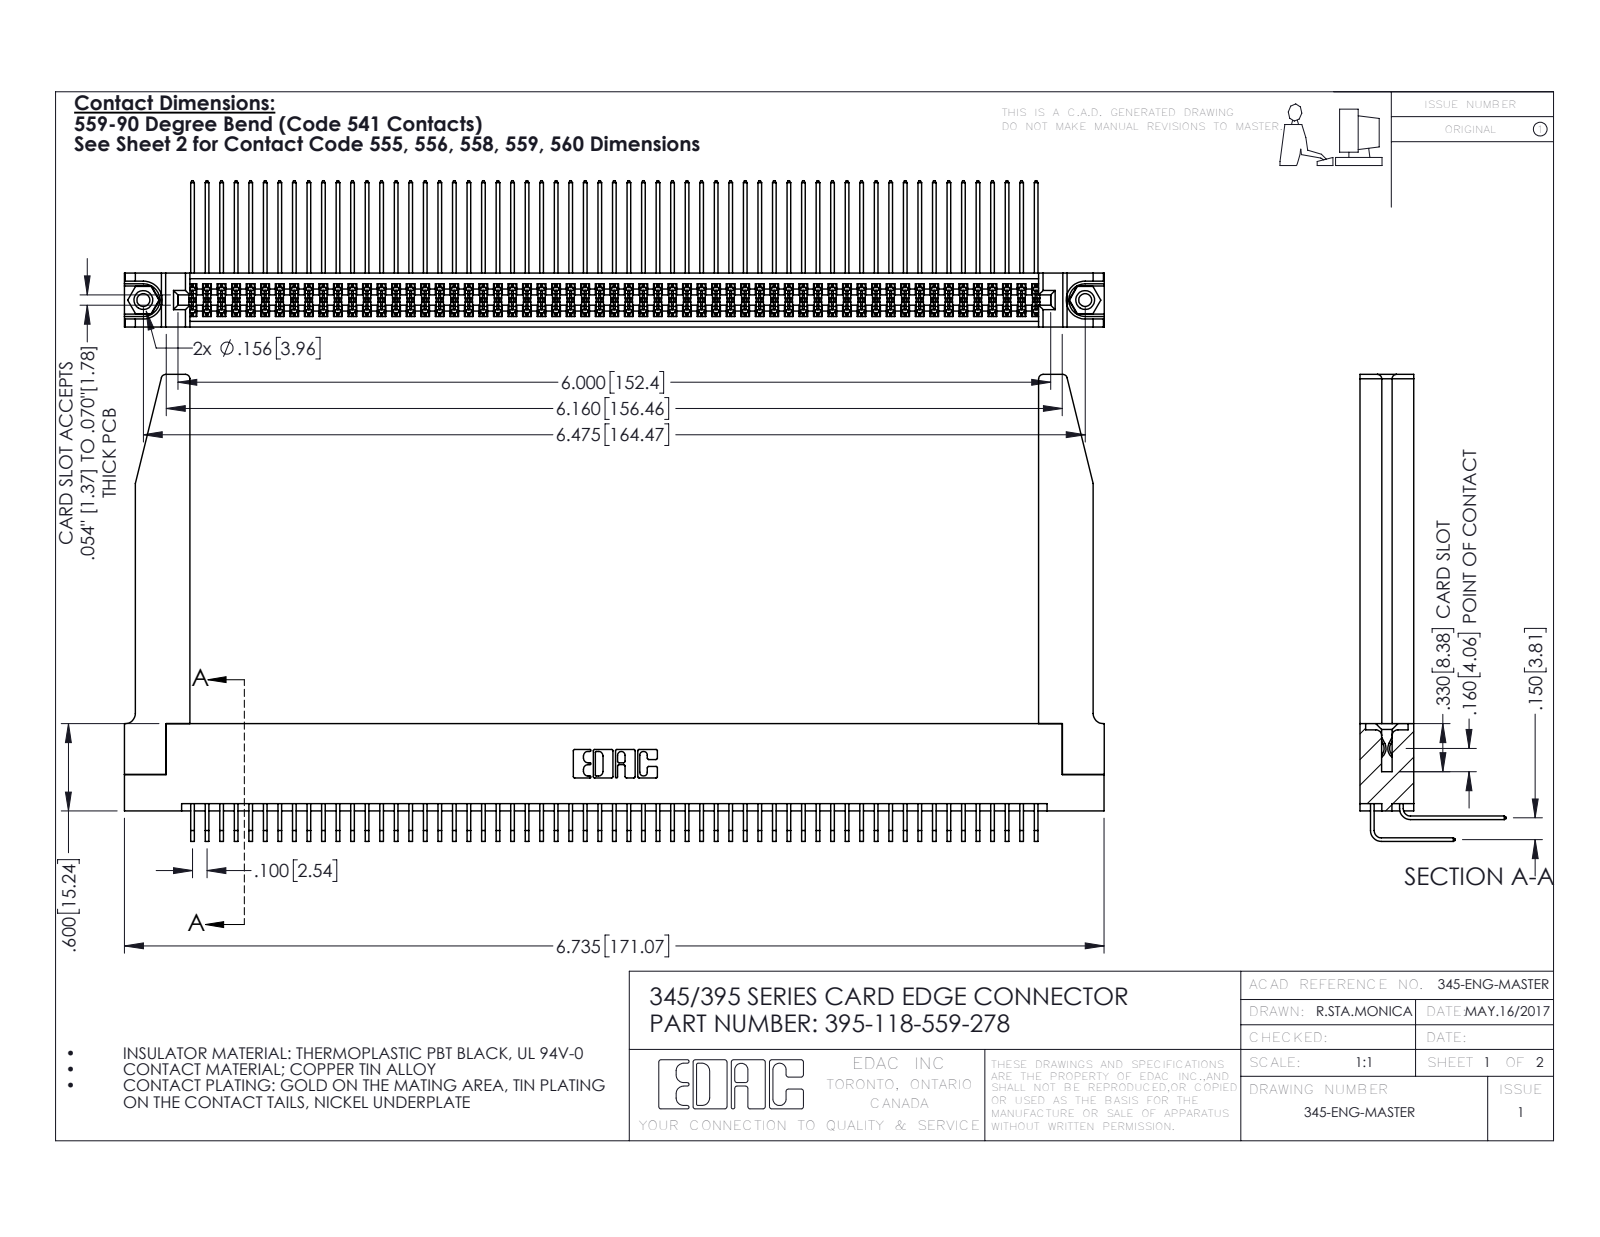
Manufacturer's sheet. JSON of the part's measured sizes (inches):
{"part_name": "395-118-559-278; 345 Part_Flush Mounting Lugs - 0.156 Dia-TH; 345-292-001_558 559 Tail - 1; 345-250-001_345-250-001-102 (+2 more)", "step_written_by": "SolidWorks 2016 (CONFIG_CONTROL_DESIGN)", "units": "inches", "bodies": {"solids": 123, "faces": 6496, "planar": 4352, "cylindrical": 2092, "other": 52}, "overall_size": [6.736, 3.209, 1.005], "volume_in3": 1.54, "surface_area_in2": 56.07, "round_holes": [[0.089, 2], [0.125, 2], [0.156, 2], [0.064, 1]], "round_bosses_or_shafts": [[0.155, 2]], "partial_cylinders_radius": [[0.006, 177], [0.01, 22], [0.03, 8], [0.007, 6], [0.031, 6], [0.026, 3], [0.014, 2], [0.019, 2]], "face_to_face_distances": [0.072, 0.298, 0.37, 0.2, 0.098, 0.272, 0.025, 0.225, 0.175, 0.15], "hole_center_spacings": [0.27, 6.239, 6.475]}
